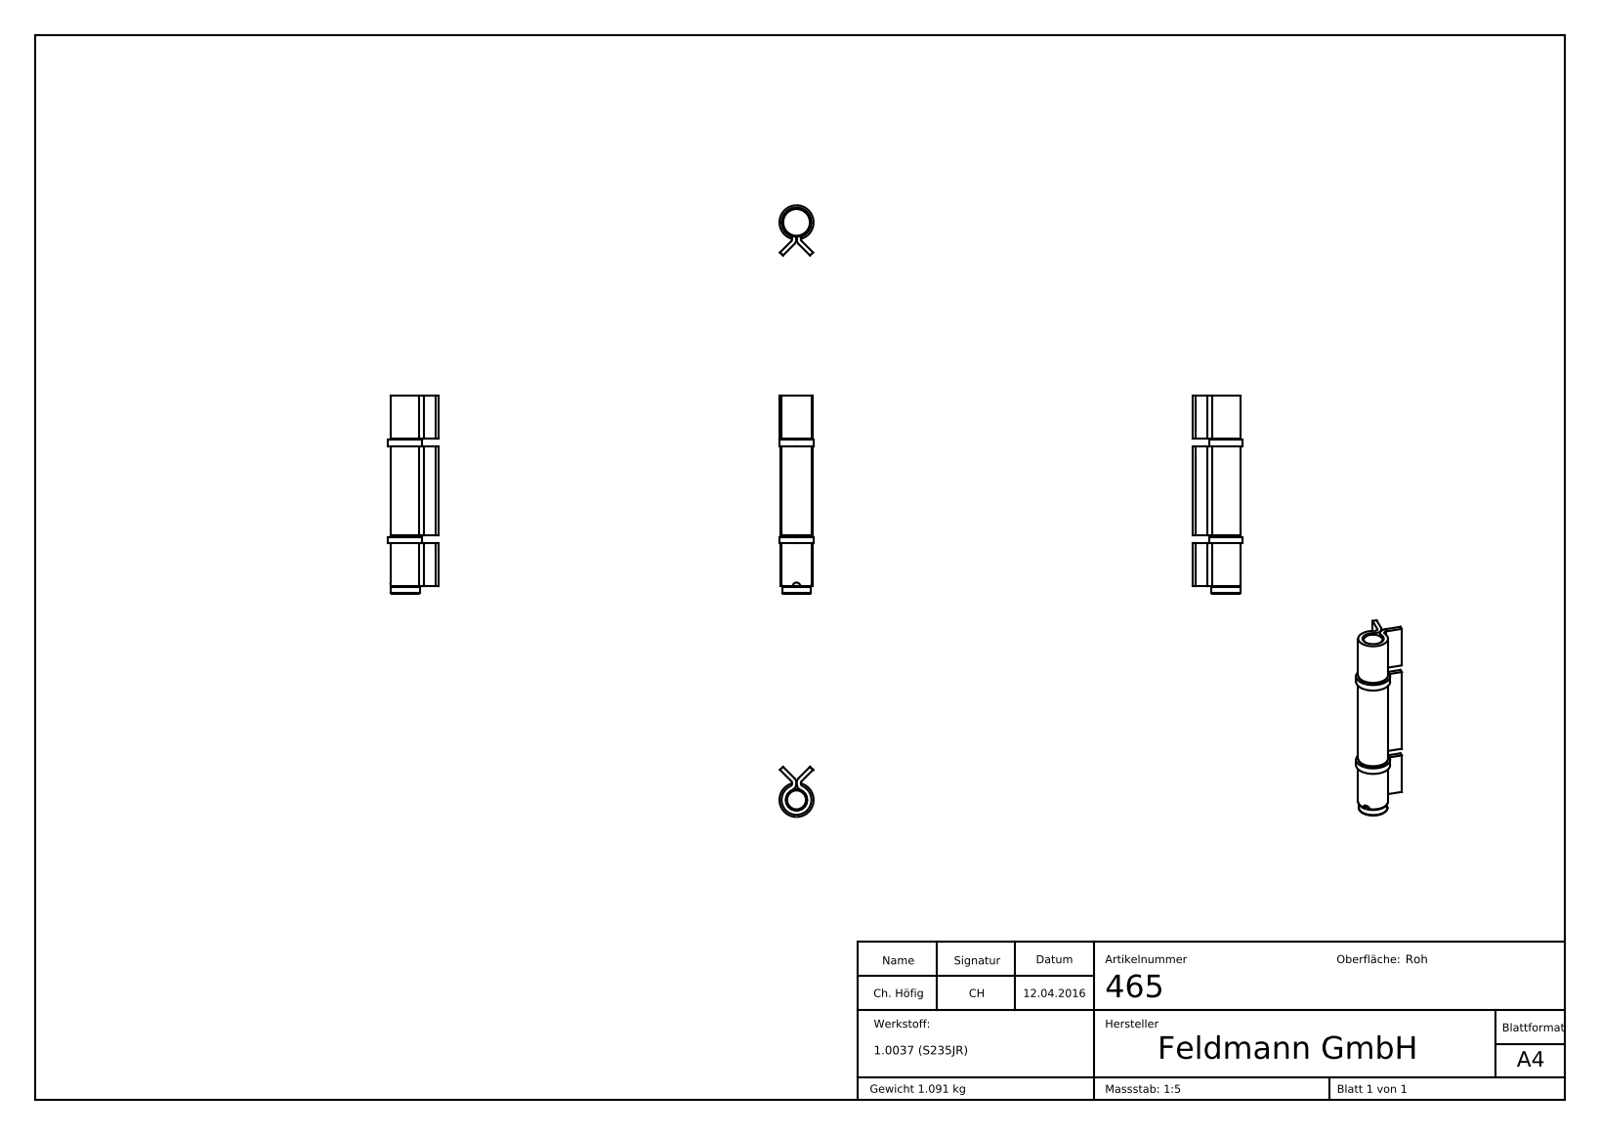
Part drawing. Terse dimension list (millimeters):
name: 465; 465 Teil2; 465 Teil3; 465 Teil4 (+2 more)
written by: SolidWorks 2018 (CONFIG_CONTROL_DESIGN)
unit: mm
bodies: 6 solids, 119 faces (34 planar, 51 cylindrical, 34 other)
size: 186 × 47 × 32
volume: 139 823 mm³; area: 58 355 mm²
holes: 1× ⌀20
bosses: 1× ⌀32, 1× ⌀28, 1× ⌀27.3, 1× ⌀27, 1× ⌀19.7
rounds: 24× R0.25, 2× R3.06, 2× R7.06, 1× R3.54
face distances: 4, 91.25, 7.25, 40, 47.25, 131.25, 138.5, 84, 98.5, 17.84
